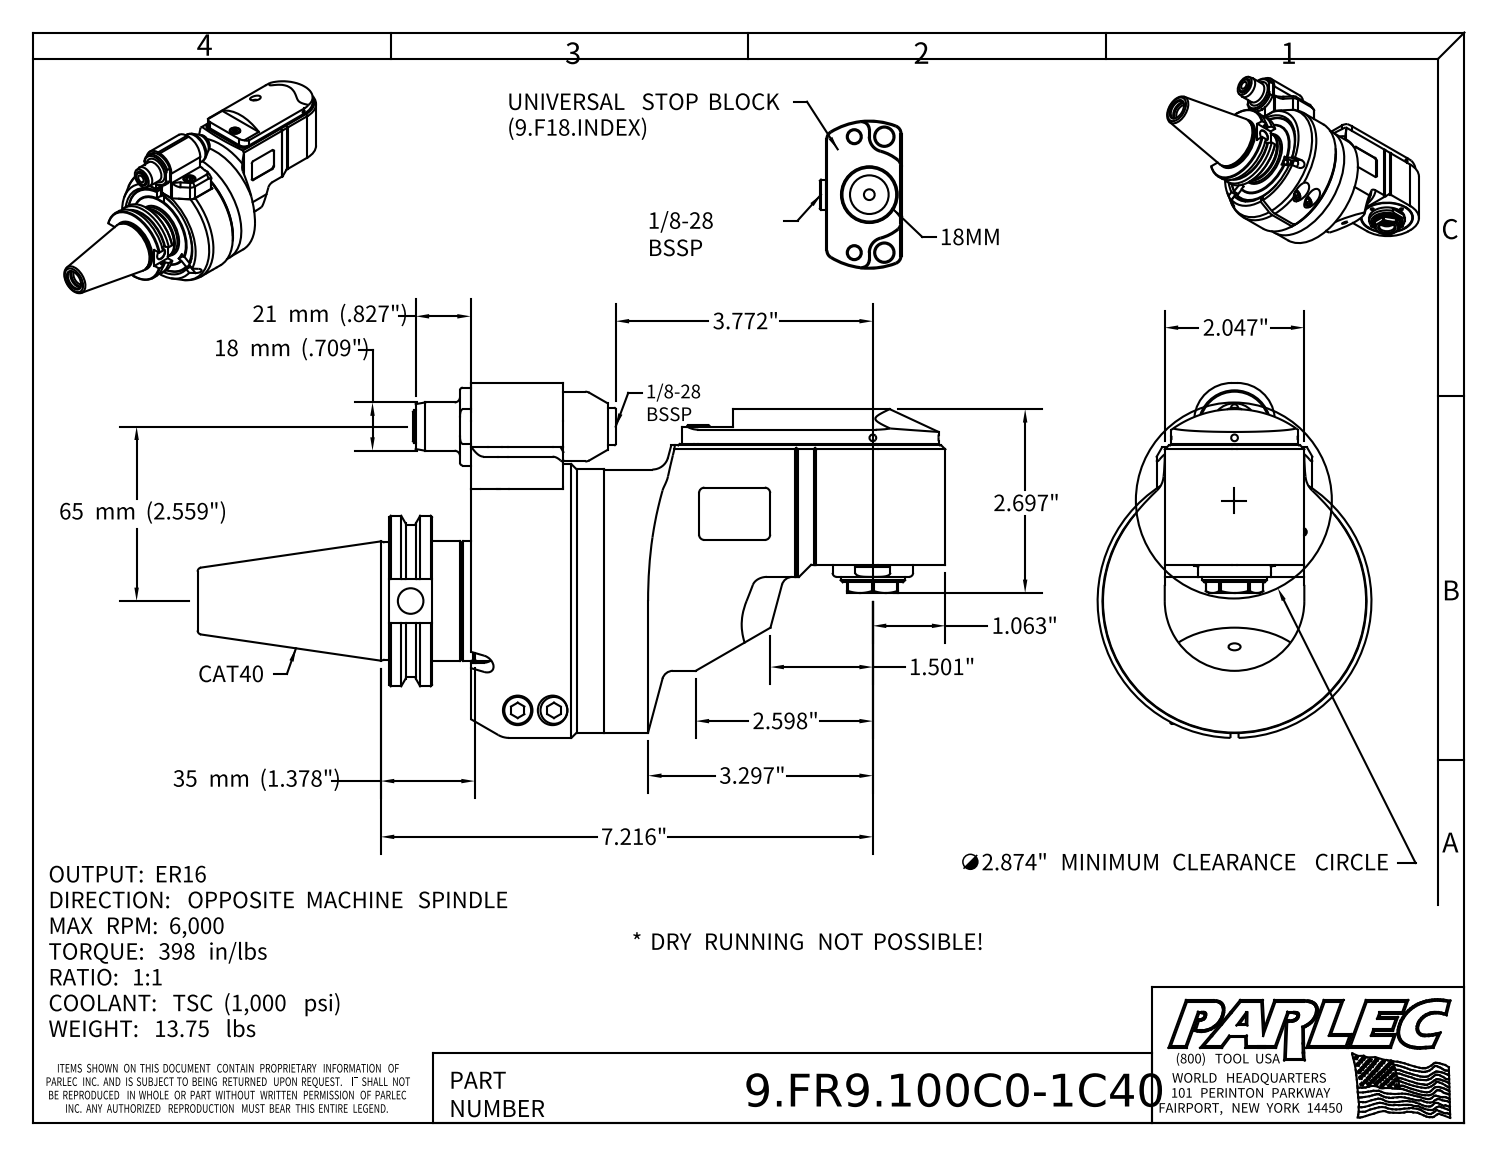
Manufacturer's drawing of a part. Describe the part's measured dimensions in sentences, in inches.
The part is named "9.FR9.100C0-1C40; 9_GA1_446_2_1_C40; 9FL1ATC; 9F18T165_ASM (+4 more)". Its 3-D file was written by "Autodesk Inventor 2022 (AUTOMOTIVE_DESIGN)". It is 5 solids with 607 faces: 263 planar, 172 cylindrical and 172 other. Overall it measures 10.966 by 5.206 by 4.016 inches. Its volume is 61.59 cubic inches and its surface area 249.5 square inches. Round holes: 22 of diameter 0.335, 10 of diameter 0.102, 7 of diameter 0.197, 3 of diameter 0.098, 3 of diameter 0.118, 3 of diameter 0.433, 2 of diameter 0.165, 2 of diameter 0.354, 2 of diameter 0.409, 2 of diameter 0.512, 1 of diameter 0.13, 1 of diameter 0.177. Round bosses or shafts: 4 of diameter 0.394, 4 of diameter 0.236, 2 of diameter 0.335, 2 of diameter 0.315, 2 of diameter 0.098, 1 of diameter 4.016, 1 of diameter 3.874, 1 of diameter 3.858. Partial cylindrical surfaces (rounded edges, fillets, slot ends): 12 of radius 0.079, 4 of radius 0.157, 2 of radius 0.02, 2 of radius 0.039, 2 of radius 0.138, 2 of radius 0.197, 2 of radius 0.236, 2 of radius 0.551. The main face-to-face distances are 0.02, 2.047, 0.276, 1.22, 0.335, 1.22, 1.083, 1.555, 0.295, 0.197. The hole center spacings are 1.496, 1.496, 0.339, 0.382, 0.689, 0.974, 1.428, 1.496.
